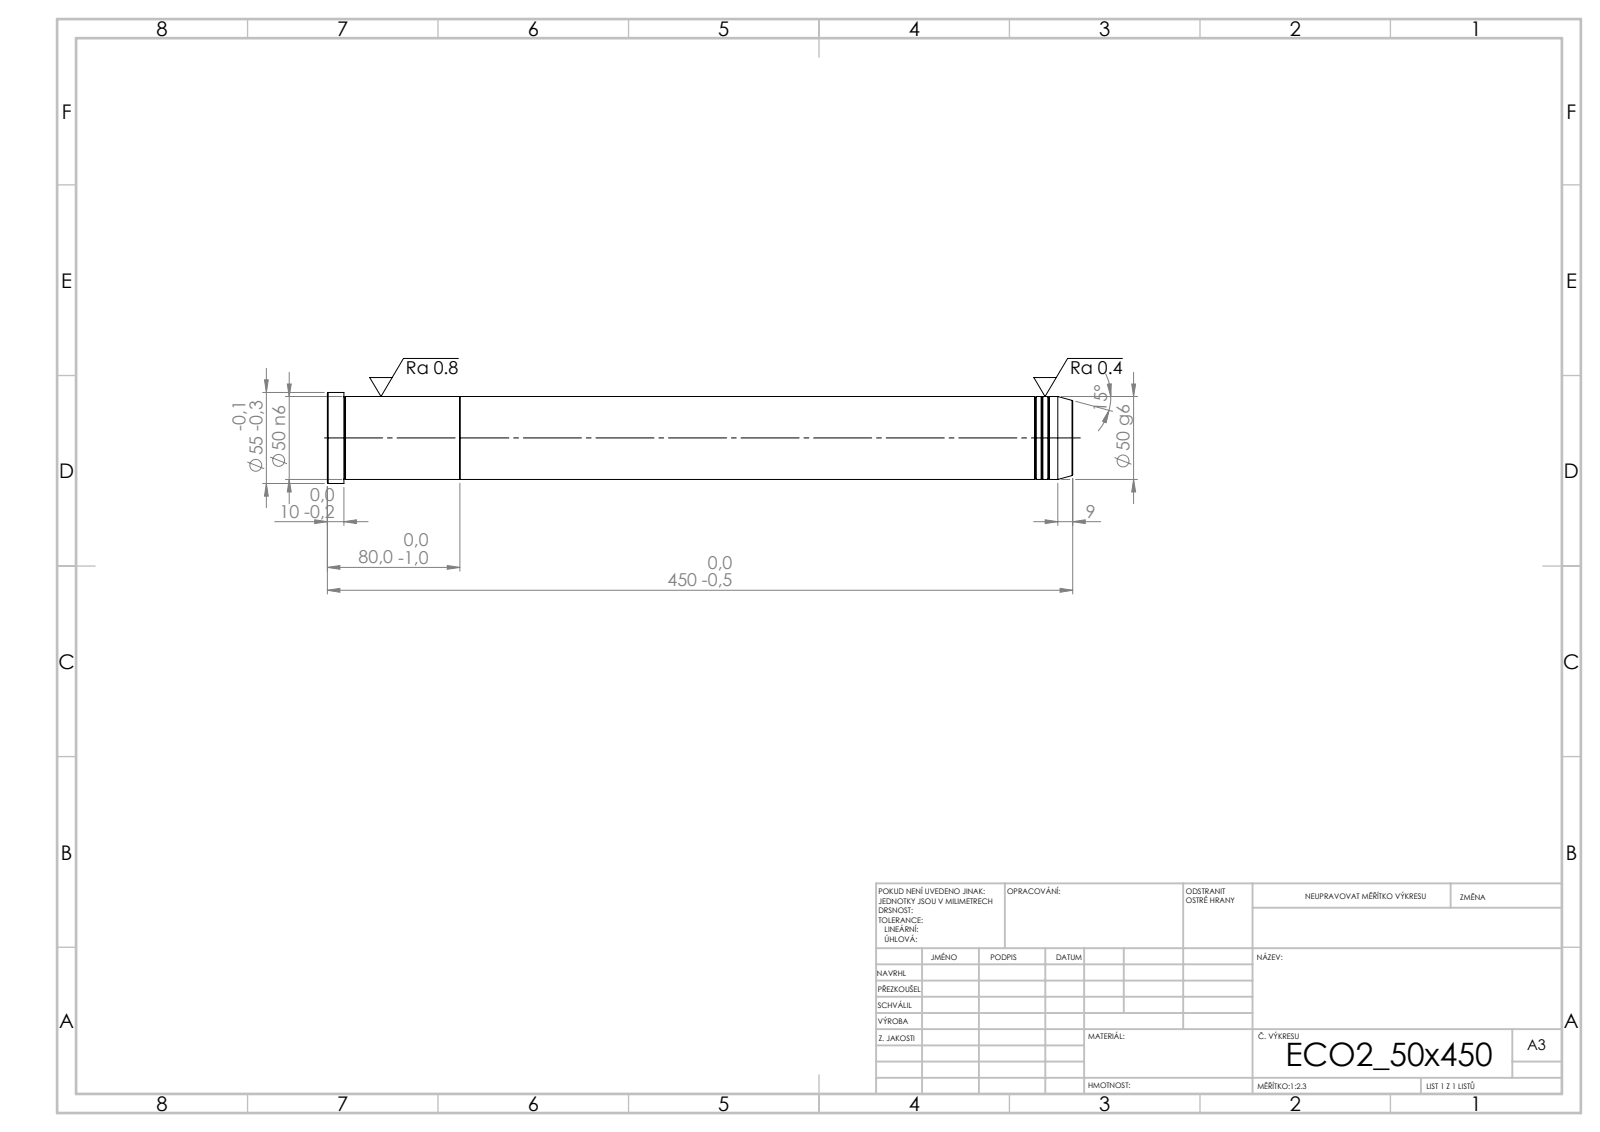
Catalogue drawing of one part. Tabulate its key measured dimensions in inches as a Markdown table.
| quantity | value |
| --- | --- |
| STEP written by | SolidWorks 2019 (CONFIG_CONTROL_DESIGN) |
| units | inches |
| bodies | 2 solids, 39 faces (5 planar, 12 cylindrical, 22 other) |
| overall size | 17.717 × 2.165 × 2.165 |
| volume | 54.05 in³ |
| surface area | 123.1 in² |
| round bosses / shafts (diameter × count) | 2.165 × 1, 1.969 × 1 |
| main face-to-face distances | 3.15, 14.567, 17.717, 17.323, 2.756, 0.394 |
